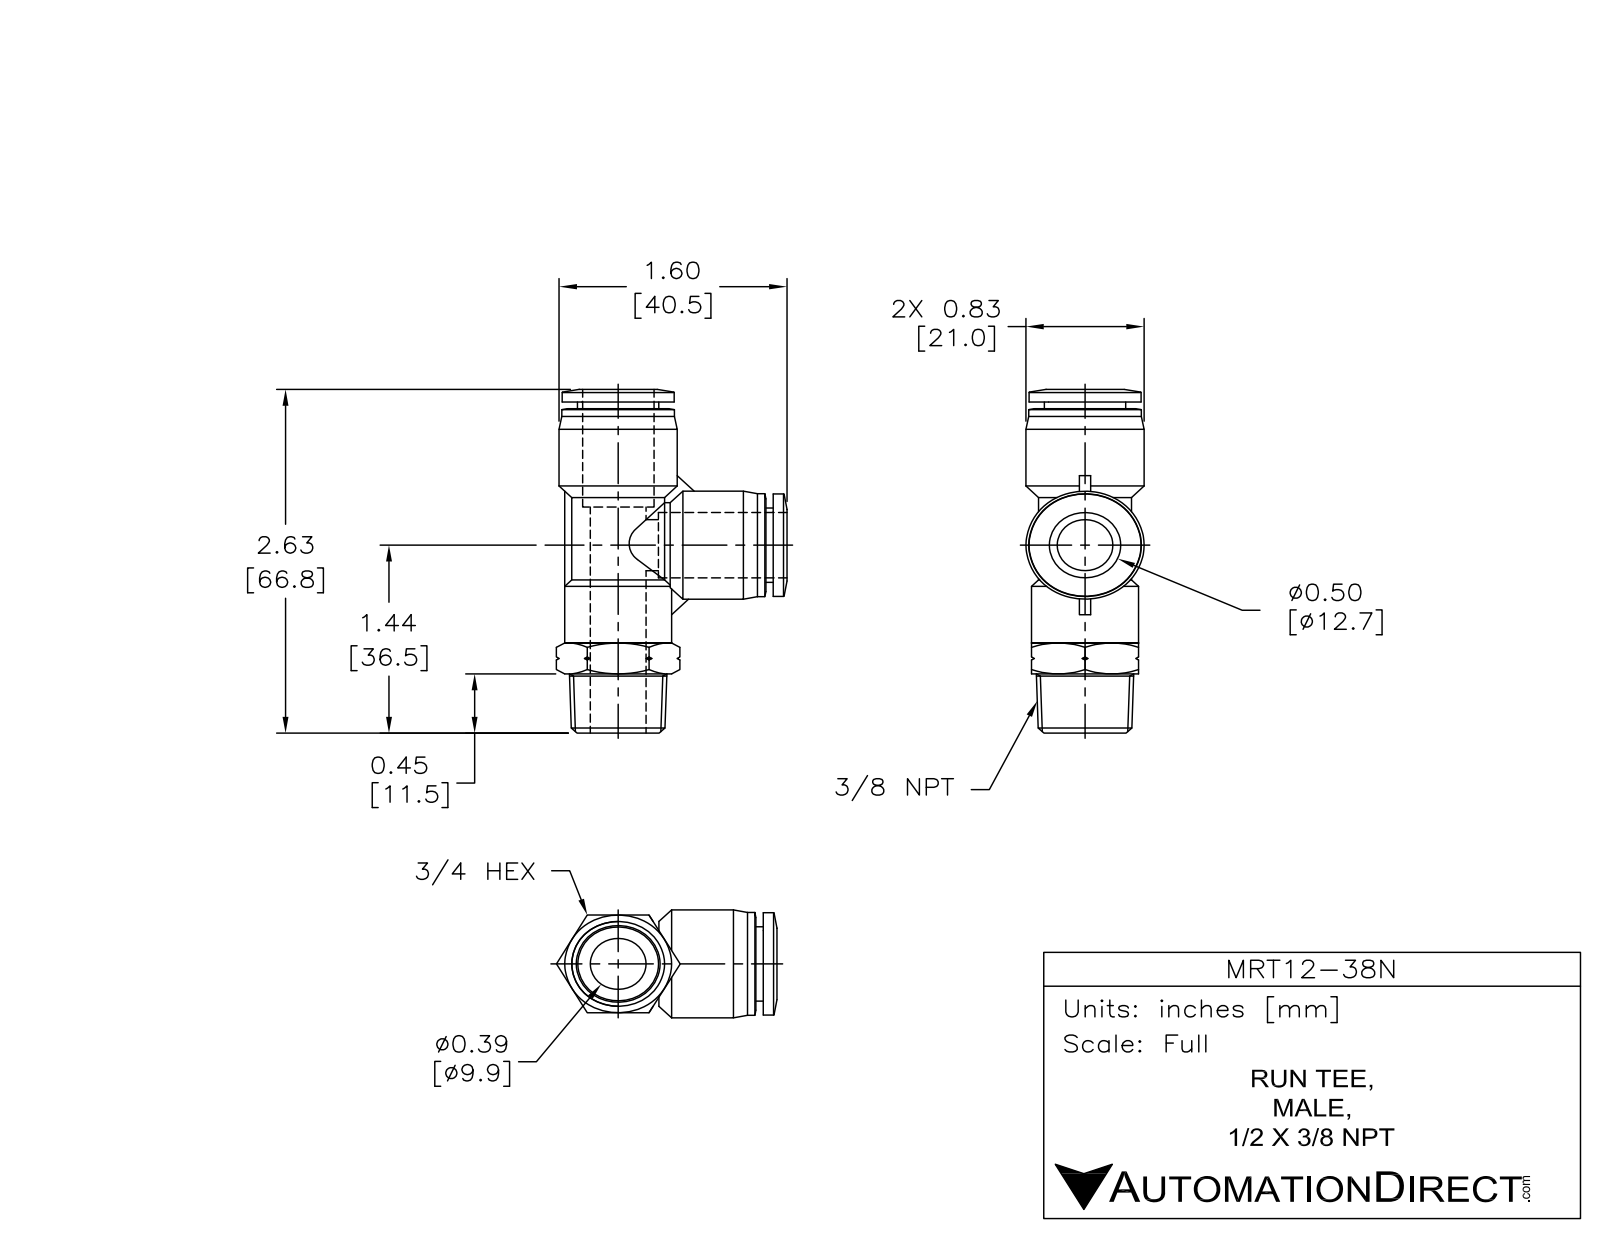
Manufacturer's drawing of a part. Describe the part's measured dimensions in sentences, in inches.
The part is named "MRT12-38N". Its 3-D file was written by "SolidWorks 2015 (AUTOMOTIVE_DESIGN)". It is 1 solid with 114 faces: 22 planar, 30 cylindrical and 62 other. Overall it measures 2.628 by 1.623 by 0.827 inches. Its volume is 0.939 cubic inches and its surface area 15.11 square inches. Round holes: 2 of diameter 0.394, 2 of diameter 0.51. Round bosses or shafts: 2 of diameter 0.827, 2 of diameter 0.787, 2 of diameter 0.783, 2 of diameter 0.65, 2 of diameter 0.569, 1 of diameter 0.748. The main face-to-face distances are 0.051, 0.748, 0.762, 0.813, 2.48, 2.531, 0.335, 0.413, 1.719, 0.453.
